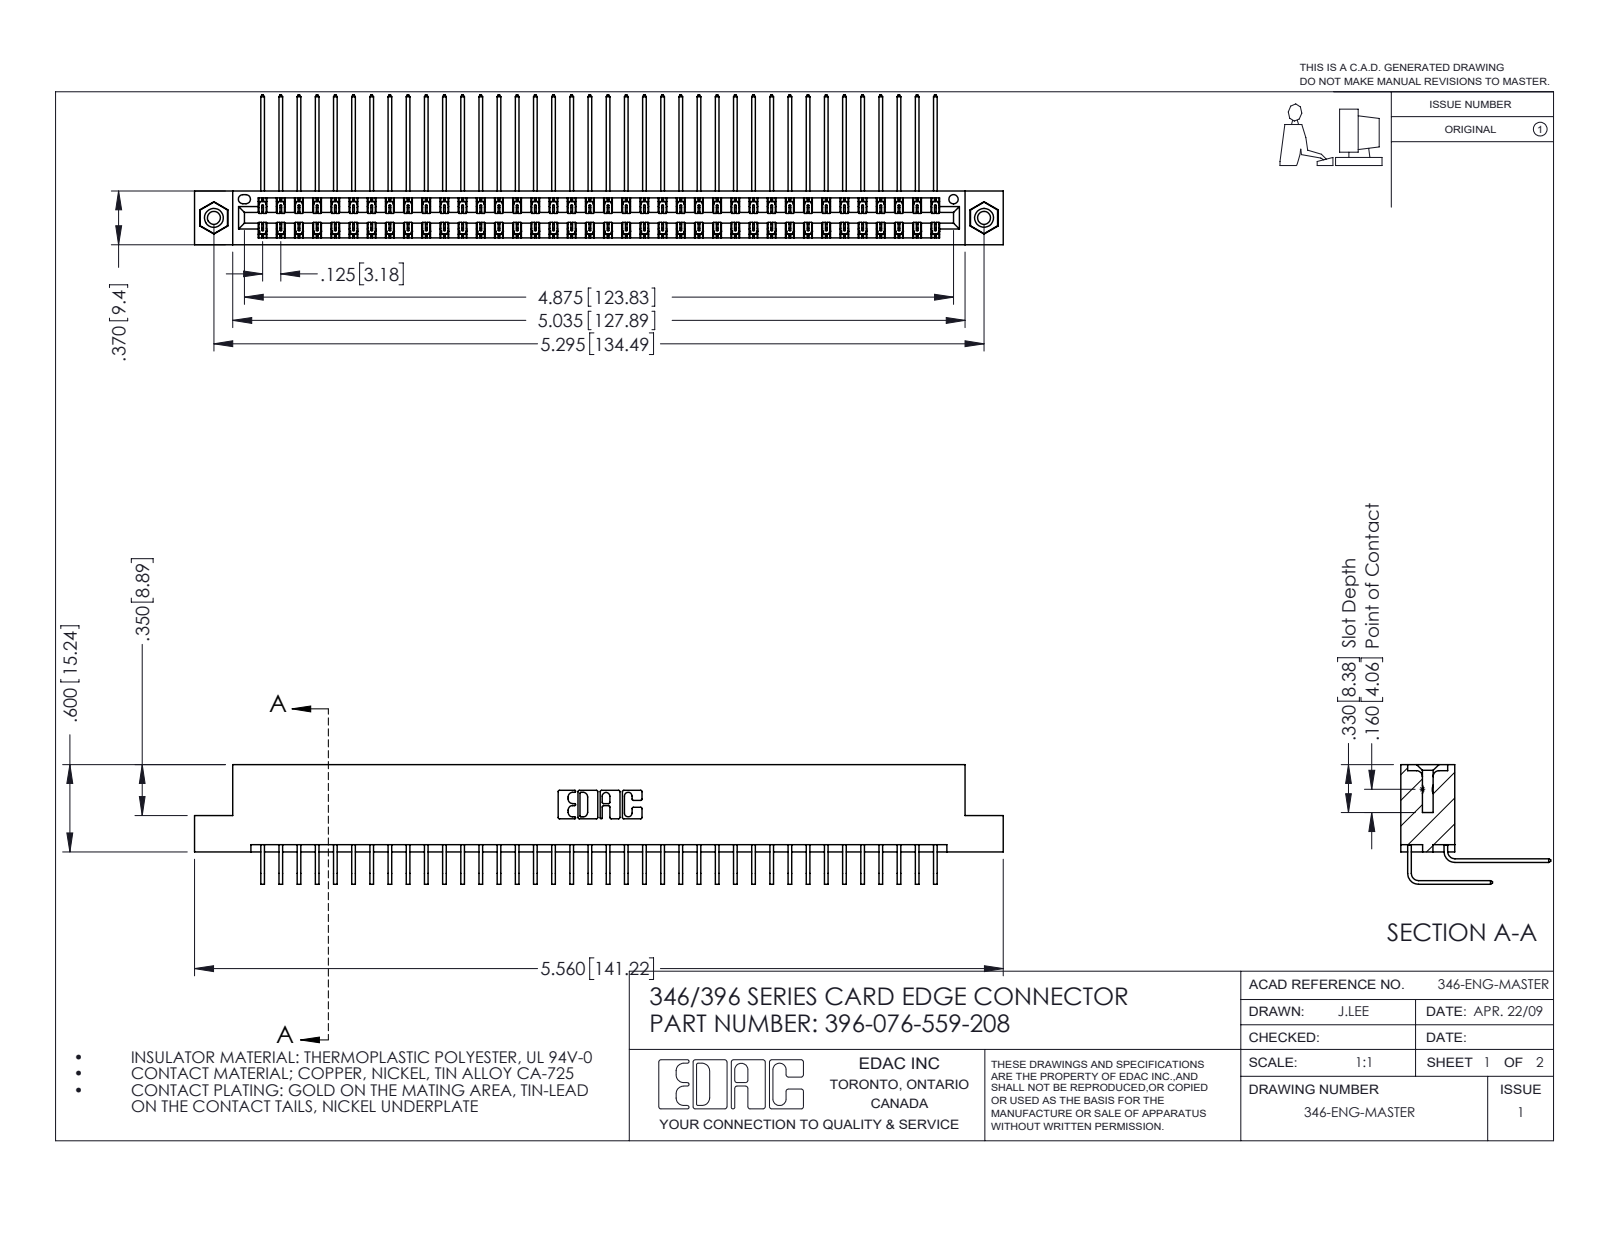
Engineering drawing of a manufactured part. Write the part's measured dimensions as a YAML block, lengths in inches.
part_name: "345-292-001_559 Tail - 2; 345-250-001_345-250-003-102; 345-292-001_558 559 Tail - 1; 346 Part_Flush Mounting Lugs - 0.156 Dia-TI (+1 more)"
step_written_by: "SolidWorks 2016 (CONFIG_CONTROL_DESIGN)"
units: inches
bodies: {solids: 79, faces: 4286, planar: 2920, cylindrical: 1350, other: 16}
overall_size: [5.56, 1.03, 0.823]
volume: 0.865
surface_area: 33.39
round_holes:
  - {diameter: 0.089, count: 2}
  - {diameter: 0.125, count: 2}
  - {diameter: 0.156, count: 2}
  - {diameter: 0.064, count: 1}
round_bosses_or_shafts:
  - {diameter: 0.155, count: 2}
partial_cylinders:
  - {radius: 0.006, count: 114}
  - {radius: 0.01, count: 22}
  - {radius: 0.007, count: 6}
  - {radius: 0.031, count: 6}
  - {radius: 0.026, count: 3}
  - {radius: 0.014, count: 2}
  - {radius: 0.022, count: 2}
  - {radius: 0.024, count: 2}
face_to_face_distances: [0.048, 0.322, 0.025, 0.37, 0.25, 0.072, 0.298, 0.275, 0.148, 0.222]
hole_center_spacings: [0.246, 5.086, 5.295]
